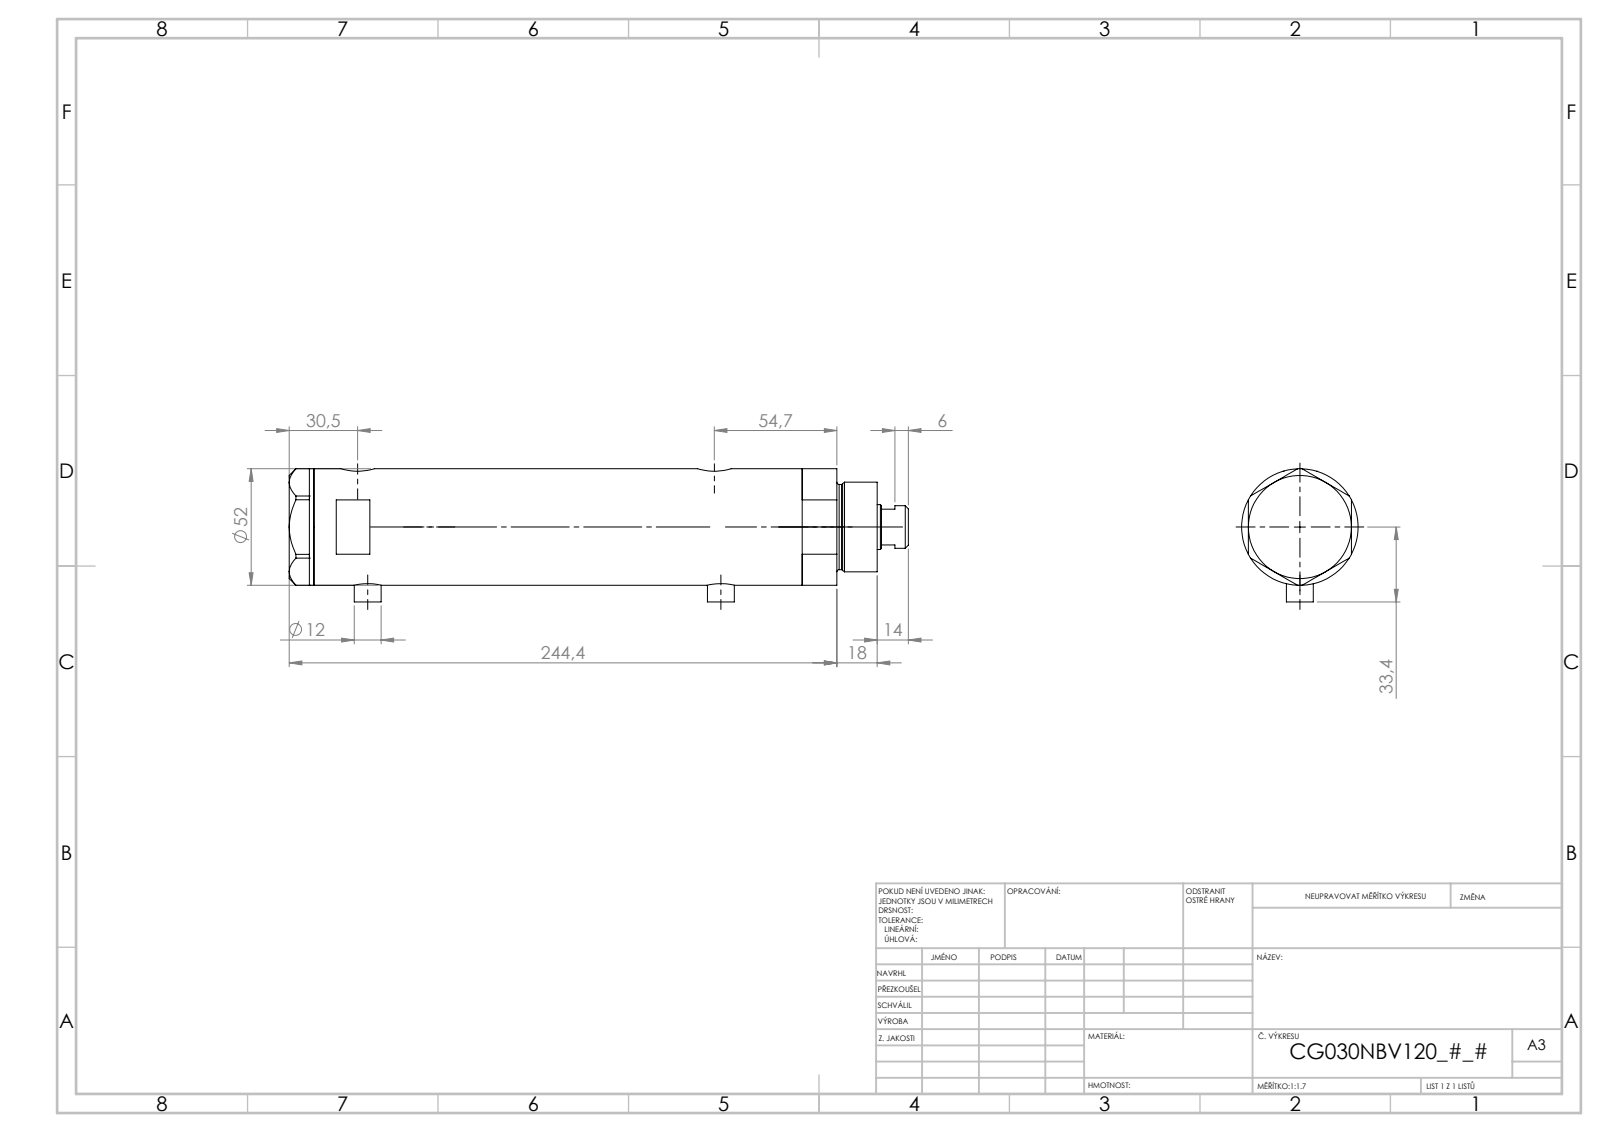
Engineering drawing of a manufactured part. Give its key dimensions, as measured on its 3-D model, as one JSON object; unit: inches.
{"part_name": "V270CG_VC; V270CG_FRONT; V270CG_MIDDLE; V270CG_BACK", "step_written_by": "SolidWorks 2019 (CONFIG_CONTROL_DESIGN)", "units": "inches", "bodies": {"solids": 4, "faces": 134, "planar": 65, "cylindrical": 49, "other": 20}, "overall_size": [10.878, 2.339, 2.047], "volume_in3": 30.03, "surface_area_in2": 164.5, "round_holes": [[0.383, 2], [0.492, 2], [0.591, 2], [0.256, 1], [0.787, 1], [0.846, 1], [1.181, 1], [1.299, 1], [1.732, 1]], "round_bosses_or_shafts": [[0.472, 2], [2.047, 1], [1.575, 1], [1.496, 1], [0.748, 1]], "face_to_face_distances": [7.146, 0.937, 6.209, 0.433, 1.37, 7.579, 1.811, 9.012, 8.579, 7.642], "hole_center_spacings": [0.114, 0.177, 6.091, 6.205, 6.268, 6.382]}
